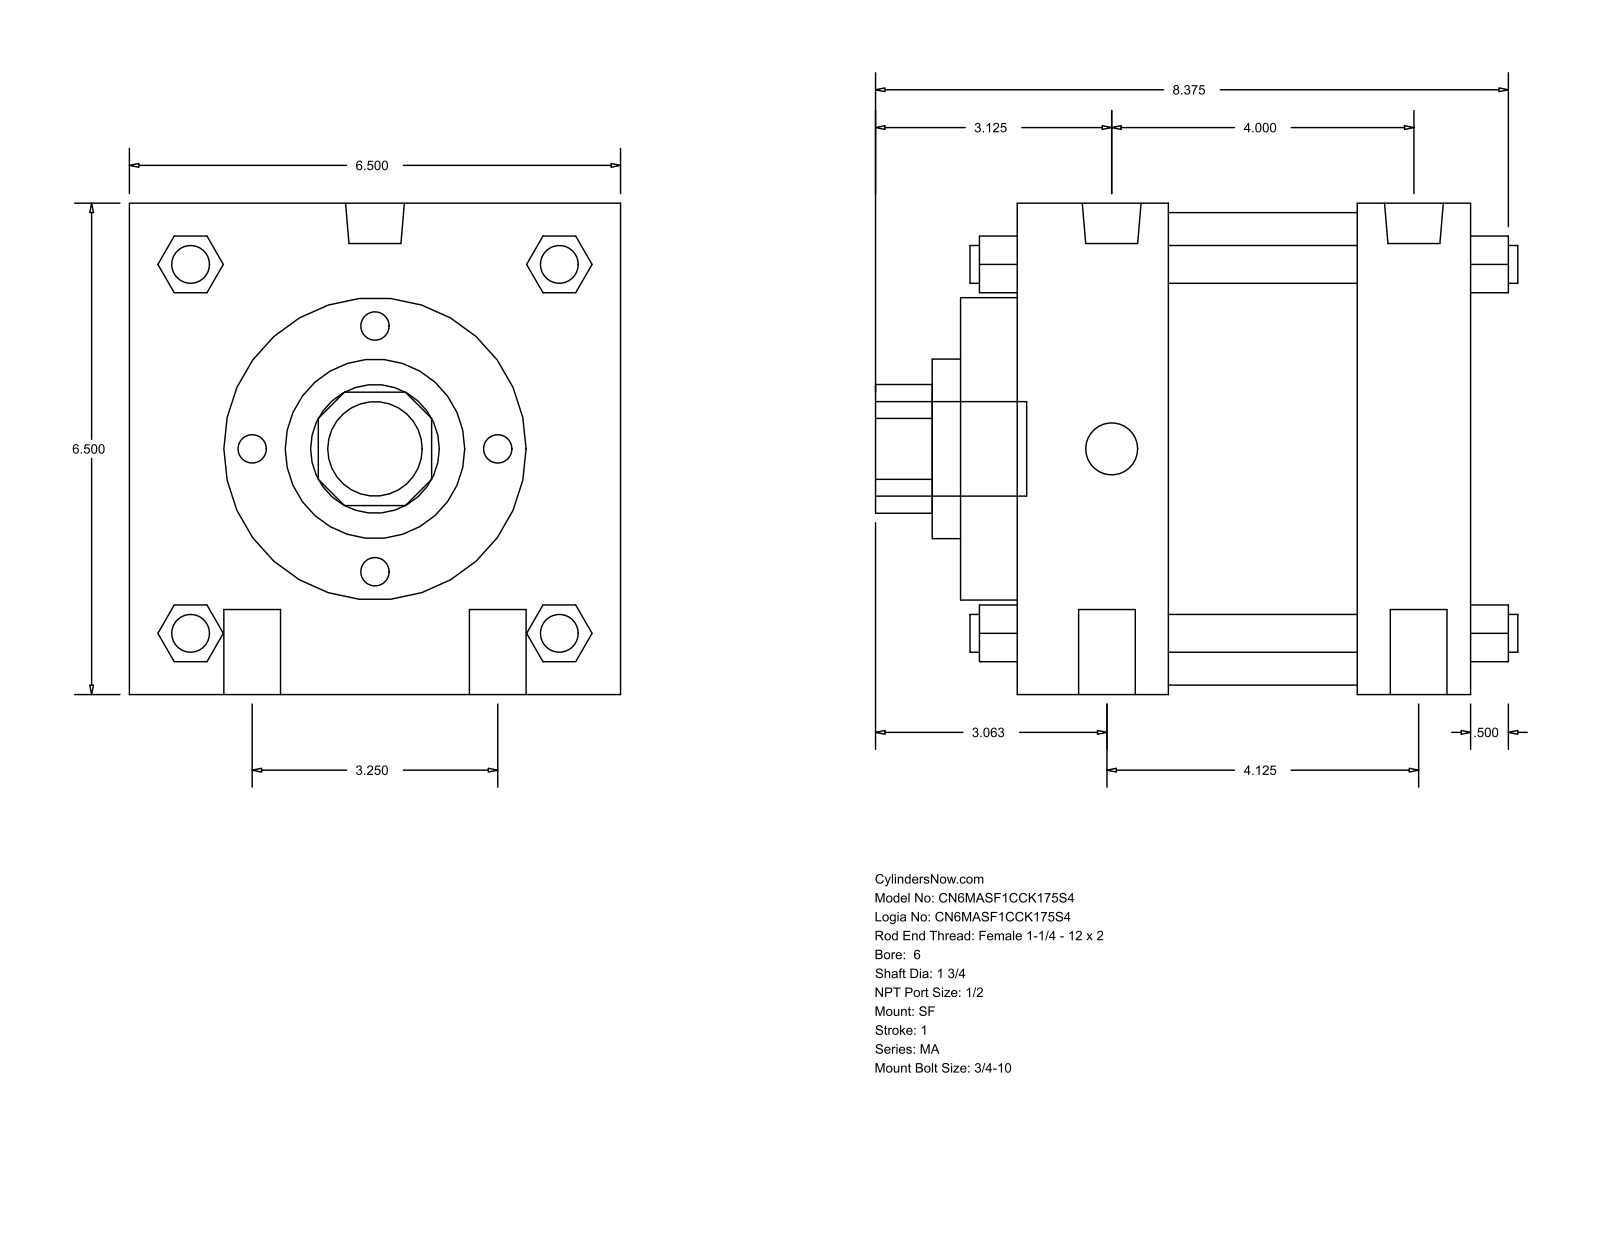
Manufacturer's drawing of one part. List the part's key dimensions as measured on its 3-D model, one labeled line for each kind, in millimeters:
Part name (STEP PRODUCT): MA_SF__0600_1.75
STEP written by: GSSL Pune (CONFIG_CONTROL_DESIGN)
Units: millimetres
Bodies: 0 solids, 126 faces (95 planar, 31 cylindrical, 0 other)
Overall size (bounding box): 215.9 × 165.1 × 165.1
Round holes (diameter × count): ⌀44.45 ×1, ⌀60.33 ×1, ⌀101.6 ×1, ⌀158.75 ×1
Round bosses / shafts (diameter × count): ⌀19.05 ×4, ⌀12.7 ×4, ⌀19.77 ×2, ⌀17.46 ×2, ⌀31.75 ×1
Partial cylindrical surfaces — rounded edges, fillets, slot ends (radius × count): R21.63 ×1
Main face-to-face distances: 165.1, 152.41, 19.05, 50.8, 38.1, 114.31, 63.51, 101.61, 69.85, 133.36
